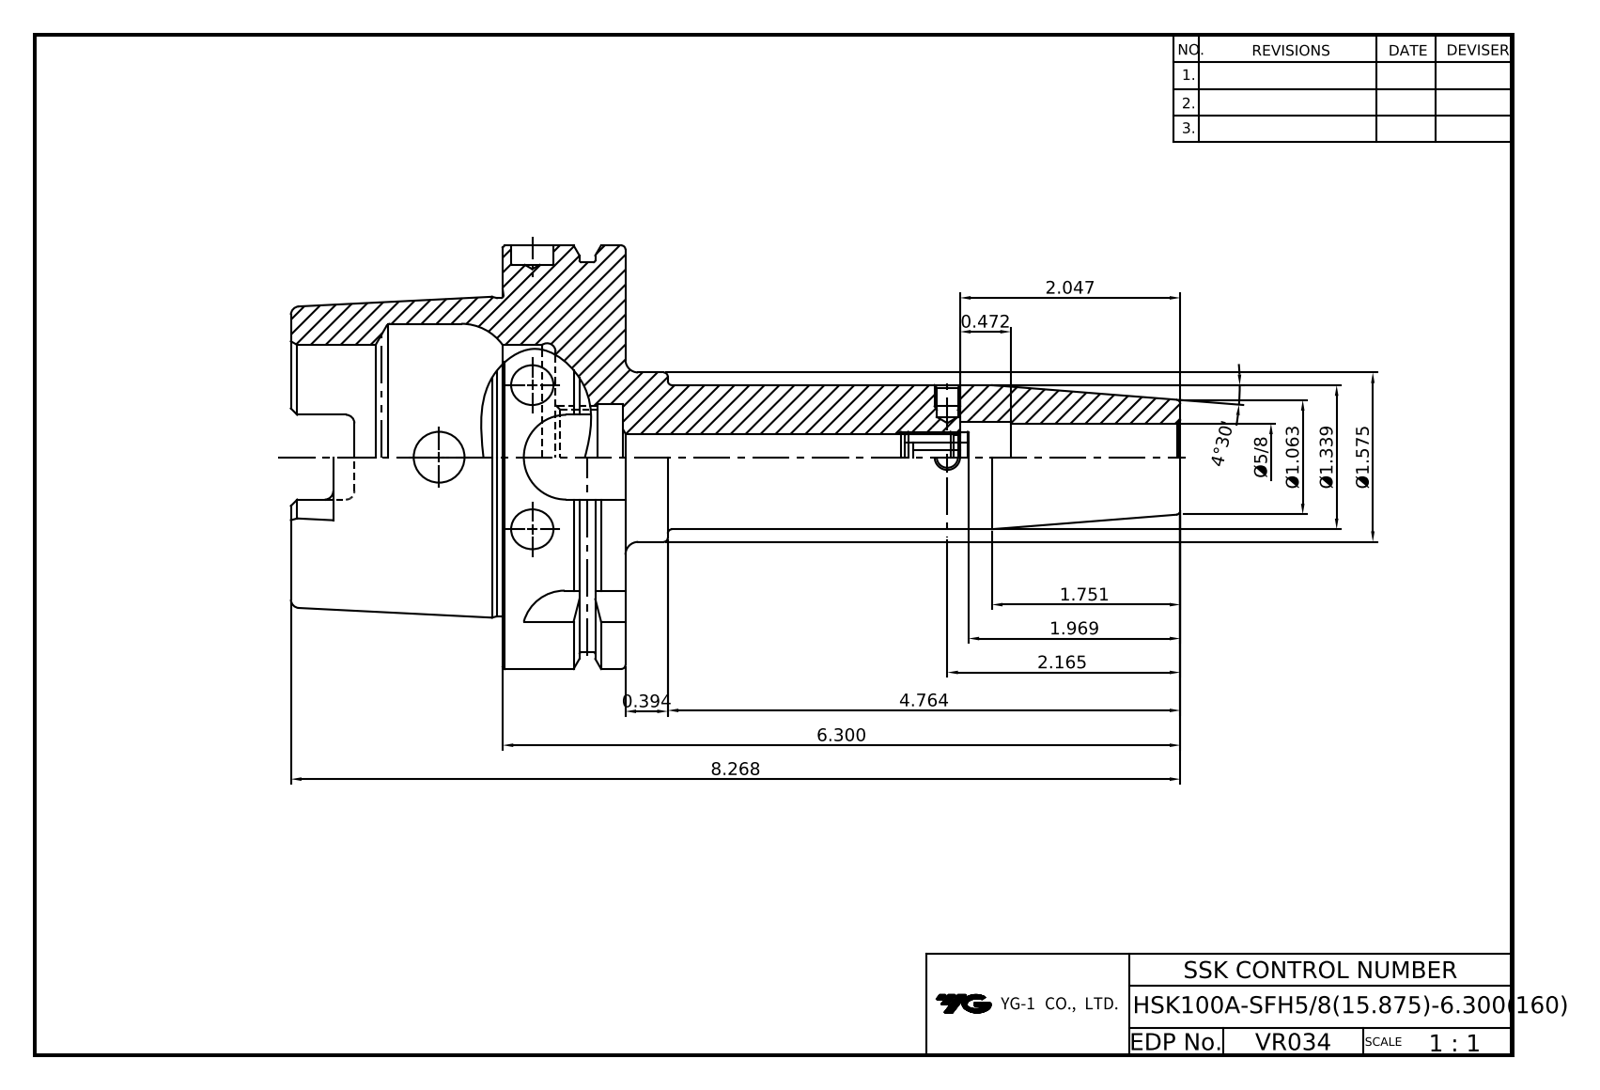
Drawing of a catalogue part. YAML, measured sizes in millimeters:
part_name: "HSK100A_SFH15_875_160"
step_written_by: "CREO PARAMETRIC BY PTC INC, 2018400 (CONFIG_CONTROL_DESIGN)"
units: millimeters
bodies: {solids: 1, faces: 213, planar: 57, cylindrical: 70, other: 86}
overall_size: [210, 100, 100]
volume: 347449
surface_area: 70316
round_holes:
  - {diameter: 5, count: 2}
  - {diameter: 6, count: 2}
  - {diameter: 10, count: 1}
  - {diameter: 11, count: 1}
  - {diameter: 11.1, count: 1}
  - {diameter: 12, count: 1}
  - {diameter: 15.87, count: 1}
  - {diameter: 16.47, count: 1}
  - {diameter: 22.5, count: 1}
  - {diameter: 24, count: 1}
  - {diameter: 25, count: 1}
  - {diameter: 53, count: 1}
round_bosses_or_shafts:
  - {diameter: 100, count: 1}
  - {diameter: 92, count: 1}
  - {diameter: 75.16, count: 1}
  - {diameter: 40, count: 1}
  - {diameter: 34, count: 1}
partial_cylinders:
  - {radius: 2, count: 6}
  - {radius: 4.88, count: 4}
  - {radius: 10, count: 4}
face_to_face_distances: [29, 12.5, 16.5, 79, 62.5, 50, 10, 72.5, 22.5, 6.5]
hole_center_spacings: [98, 120]
